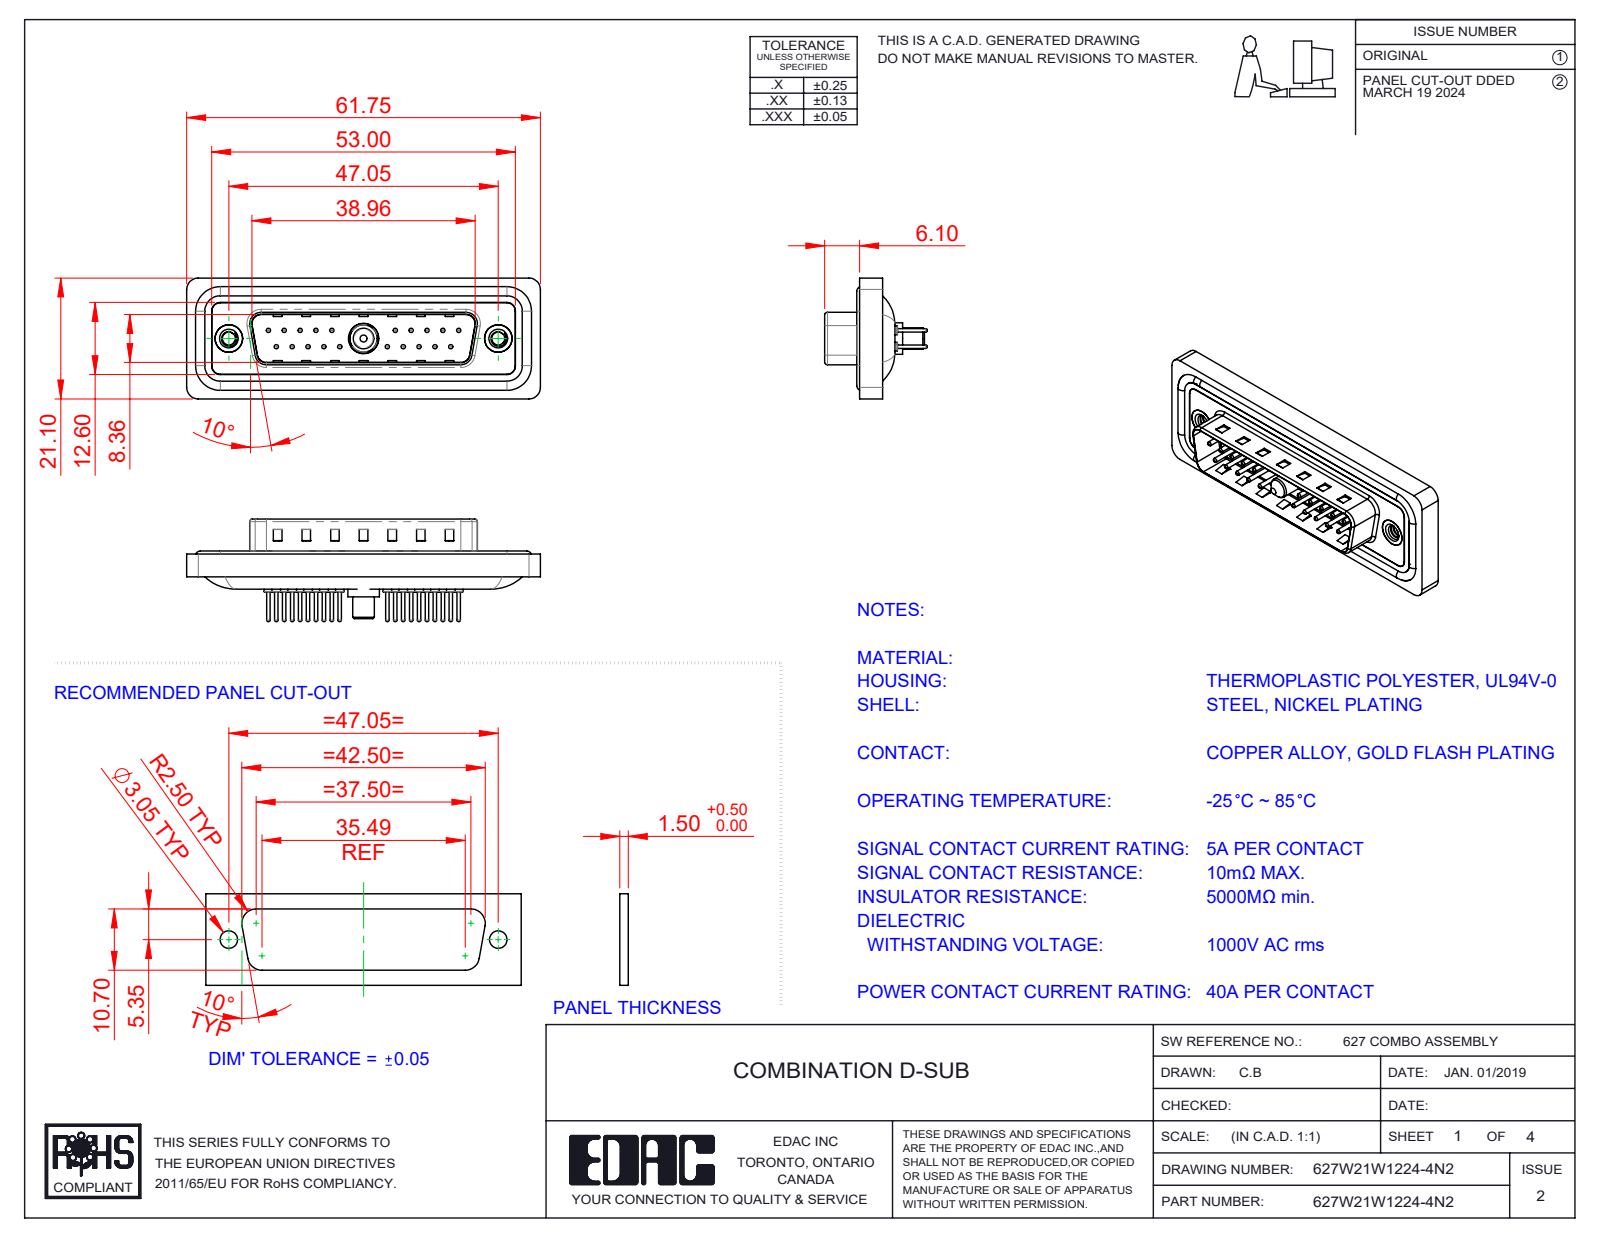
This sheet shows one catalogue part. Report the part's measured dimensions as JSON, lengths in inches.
{"part_name": "Power Pin_40A S; 627Combo Threaded Rivet_2; 627Combo Contact Row 2_24; 627W21W1224-4N2 (+5 more)", "step_written_by": "SolidWorks 2023 (CONFIG_CONTROL_DESIGN)", "units": "inches", "bodies": {"solids": 29, "faces": 1262, "planar": 359, "cylindrical": 487, "other": 416}, "overall_size": [2.431, 0.831, 0.705], "volume_in3": 0.44, "surface_area_in2": 18.54, "round_holes": [[0.03, 20], [0.063, 20], [0.079, 20], [0.089, 2], [0.157, 2], [0.189, 2], [0.197, 2], [0.191, 1], [0.209, 1]], "round_bosses_or_shafts": [[0.059, 20], [0.024, 20], [0.063, 4], [0.193, 2], [0.217, 1], [0.205, 1], [0.187, 1], [0.148, 1]], "partial_cylinders_radius": [[0.059, 22], [0.079, 18], [0.02, 8], [0.063, 8], [0.01, 4], [0.024, 4], [0.026, 4], [0.035, 4]], "face_to_face_distances": [0.016, 0.059, 0.043, 0.063, 0.02, 0.122, 0.114, 0.161, 0.032, 0.377], "hole_center_spacings": [0.124, 0.109, 0.218, 0.327, 0.198, 0.763, 0.826, 0.872]}
